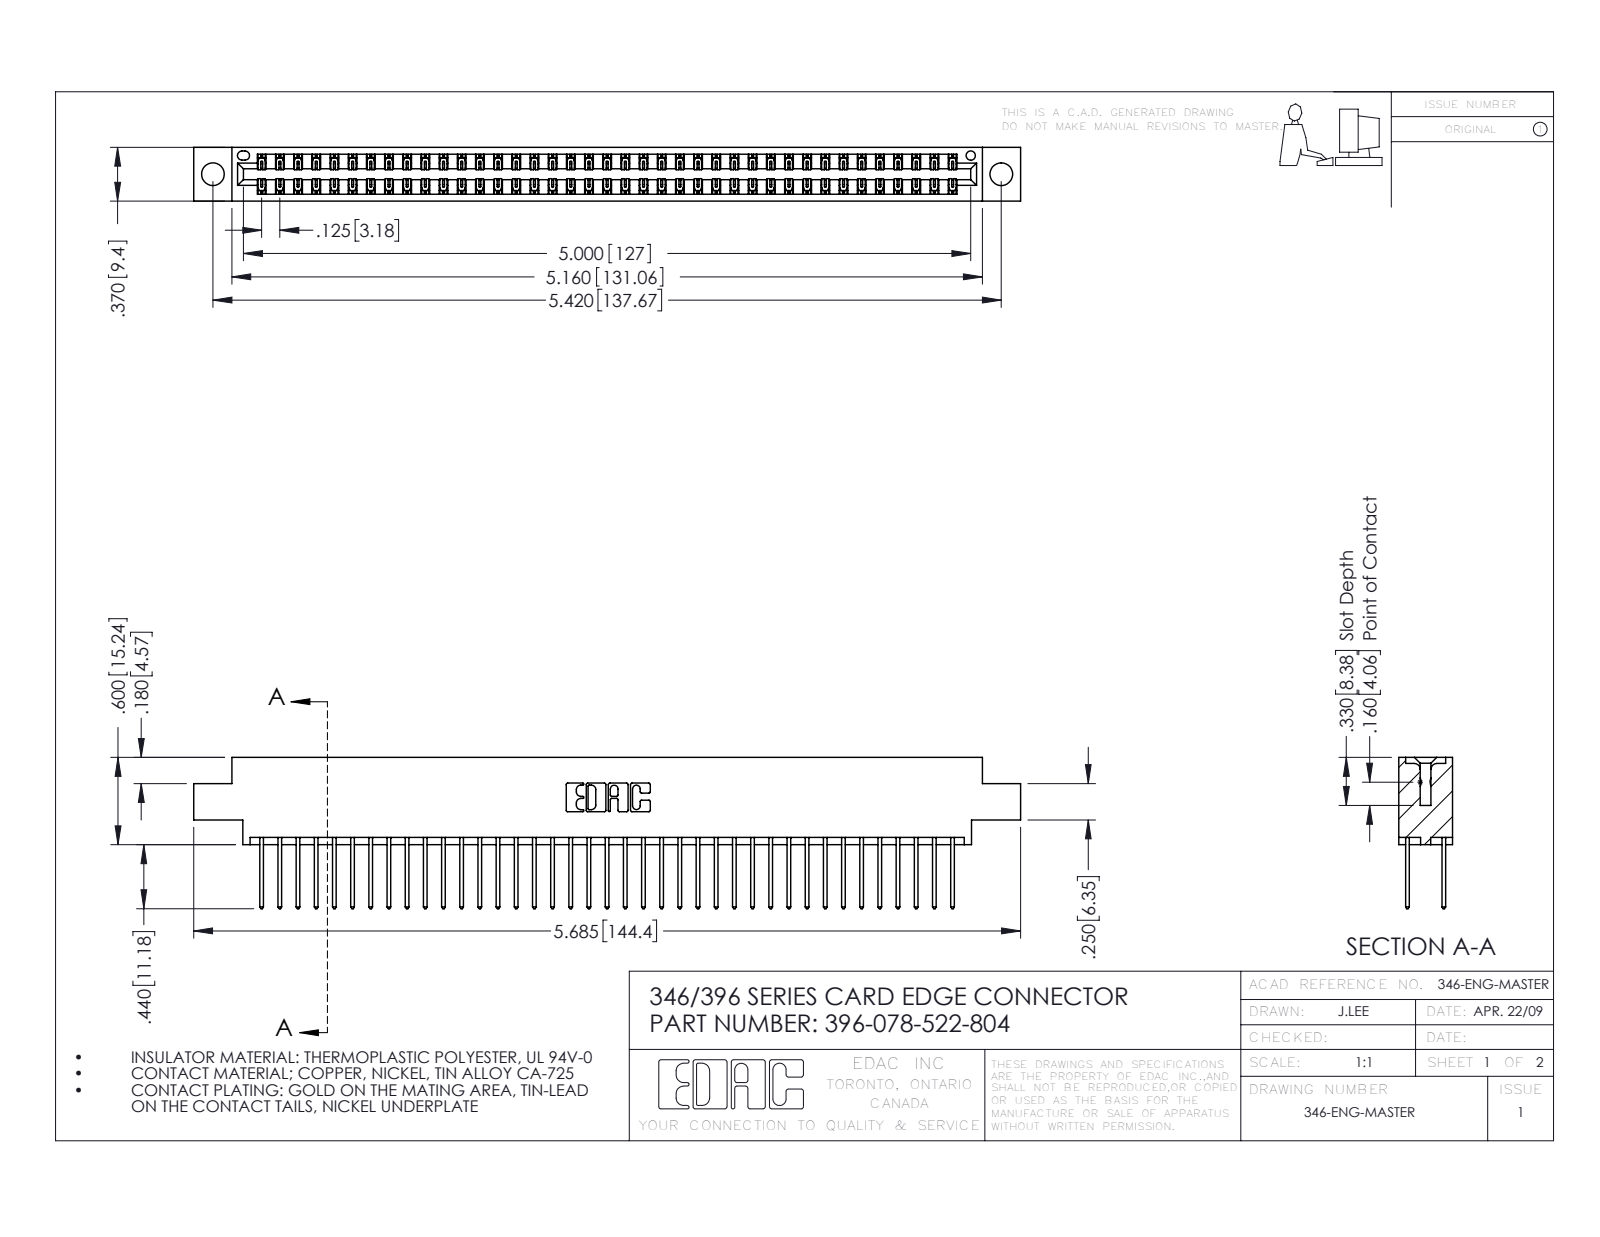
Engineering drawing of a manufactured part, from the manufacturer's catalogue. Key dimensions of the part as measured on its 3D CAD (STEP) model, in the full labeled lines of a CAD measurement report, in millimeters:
Part name (STEP PRODUCT): 345-292-001_345-293-122; 396-078-522-804; 346 Part_0.170 Offset - 0.156 Dia-TH
STEP written by: SolidWorks 2016 (CONFIG_CONTROL_DESIGN)
Units: millimetres
Bodies: 79 solids, 4182 faces (2810 planar, 1372 cylindrical, 0 other)
Overall size (bounding box): 144.4 × 26.4 × 9.4
Volume: 14 000 mm³ · Surface area: 20 140 mm²
Round holes (diameter × count): ⌀4 ×2, ⌀1.6 ×1
Partial cylindrical surfaces — rounded edges, fillets, slot ends (radius × count): R0.2 ×117, R0.3 ×78, R0.3 ×22, R0.2 ×6, R0.8 ×6, R0.7 ×3, R0.4 ×2, R0.6 ×2
Main face-to-face distances: 1.2, 8.2, 6.4, 9.4, 1.8, 7.6, 0.6, 7, 3.8, 5.6
Hole centre spacings: 6.2, 132.4, 137.7
